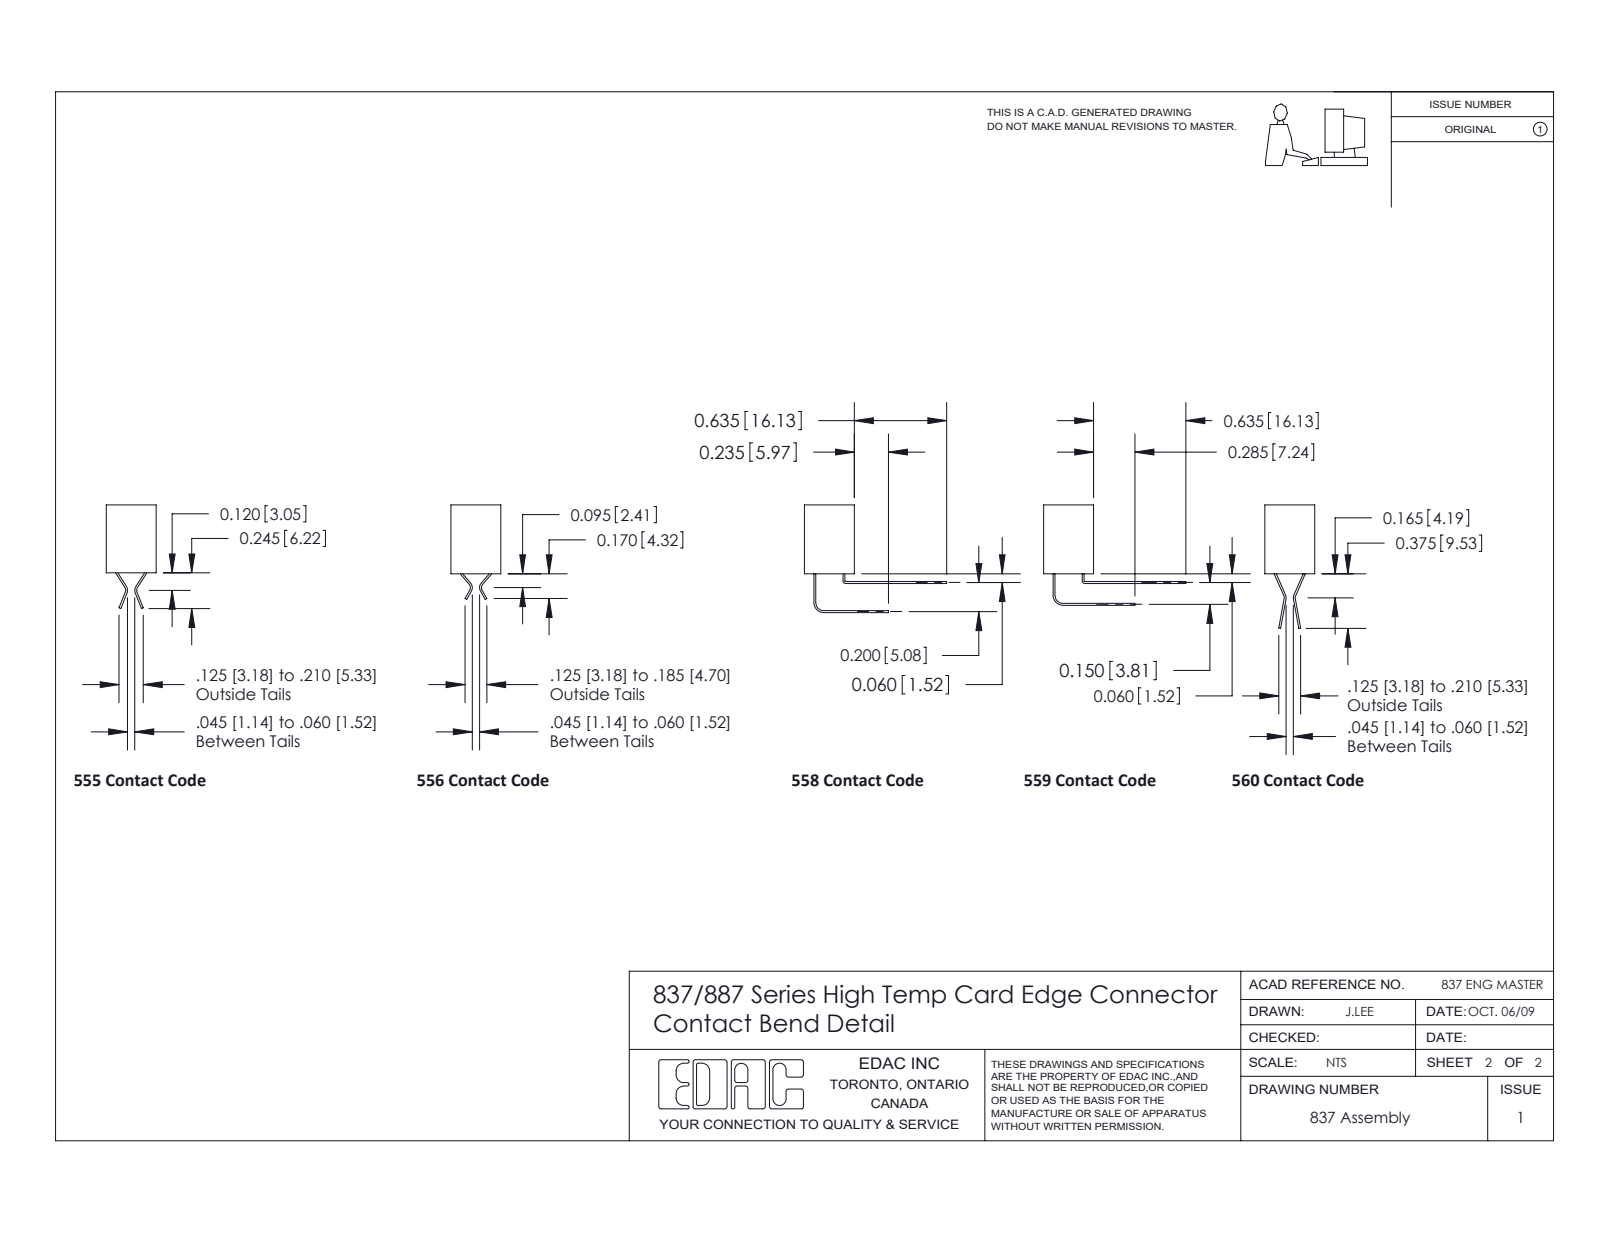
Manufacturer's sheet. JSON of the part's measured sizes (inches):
{"part_name": "337 Part_Flush Mounting Lugs - 0.156 Dia-TH; 345-250-002_345-250-002-102; 345-292-001_345-293-120; 337-015-520-103", "step_written_by": "SolidWorks 2016 (CONFIG_CONTROL_DESIGN)", "units": "inches", "bodies": {"solids": 18, "faces": 1142, "planar": 800, "cylindrical": 334, "other": 8}, "overall_size": [3.246, 0.788, 0.37], "volume_in3": 0.501, "surface_area_in2": 13.03, "round_holes": [[0.116, 2], [0.156, 2]], "round_bosses_or_shafts": [[0.25, 2], [0.18, 2], [0.136, 2]], "partial_cylinders_radius": [[0.01, 32], [0.006, 30], [0.01, 22], [0.007, 6], [0.031, 6], [0.026, 3], [0.014, 1], [0.022, 1]], "face_to_face_distances": [0.37, 0.298, 0.072, 0.149, 0.2, 0.072, 0.025, 0.098, 0.272, 0.225], "hole_center_spacings": [2.936]}
